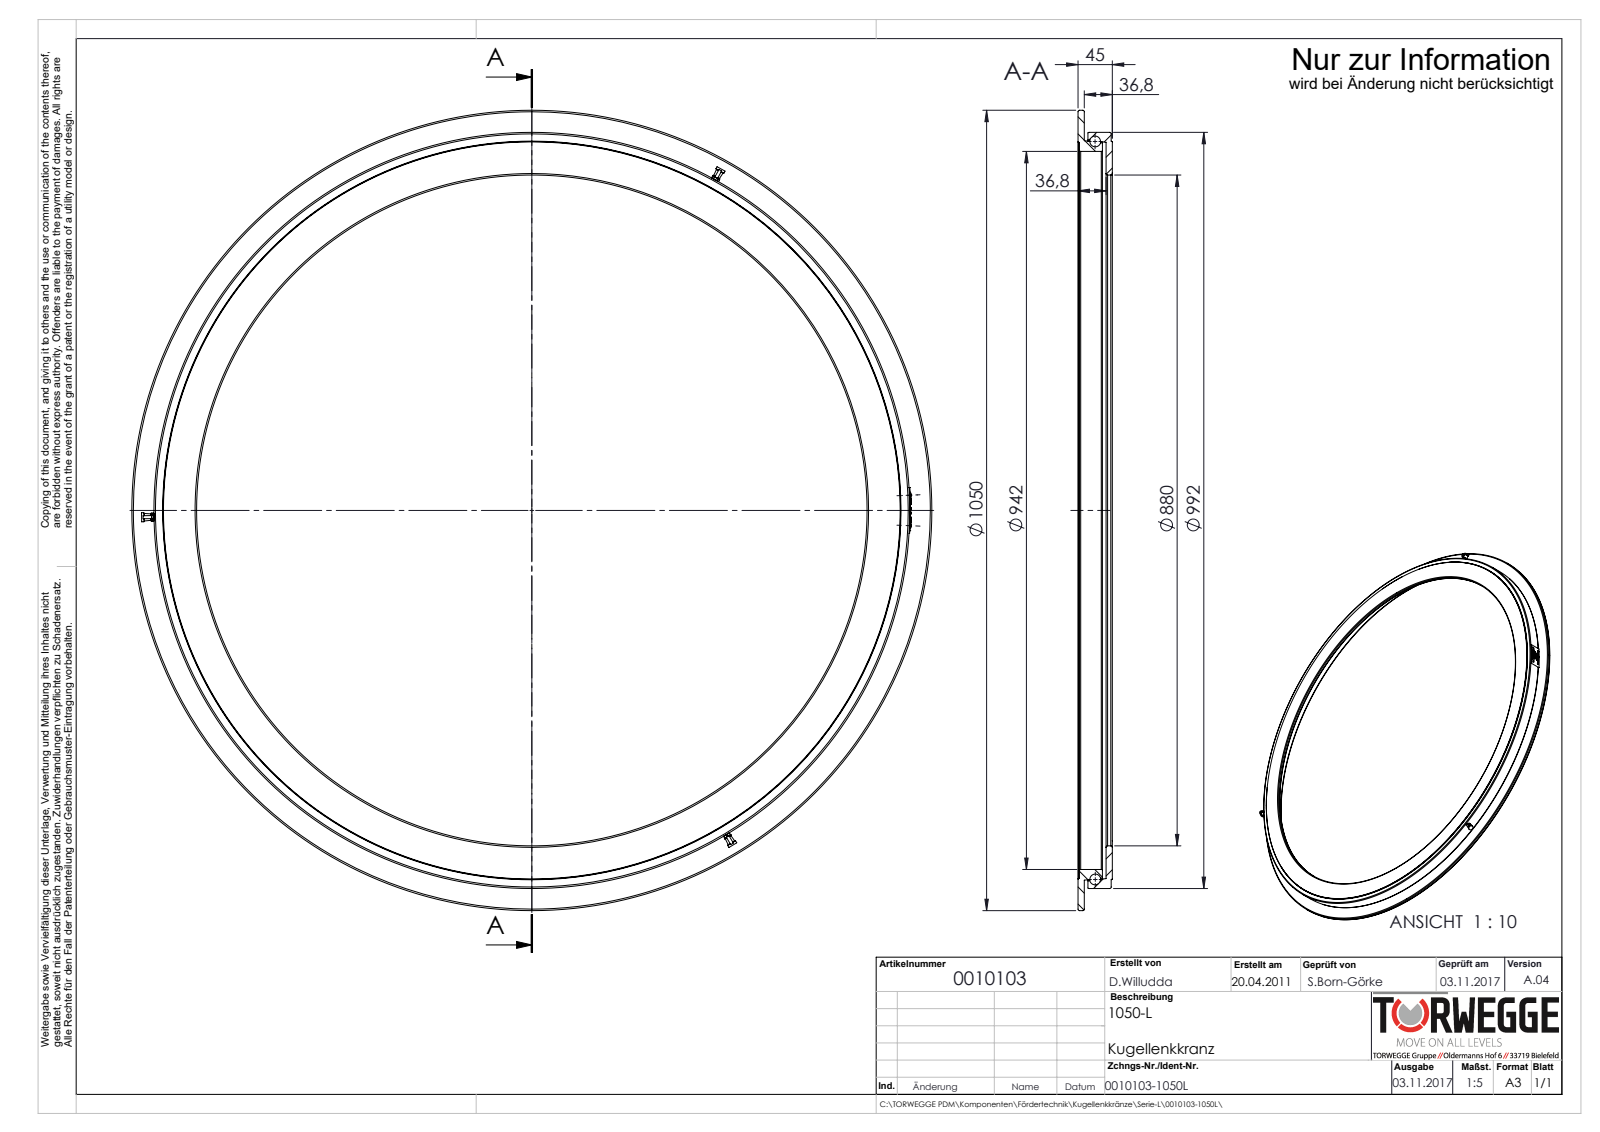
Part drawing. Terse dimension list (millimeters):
name: NT-0004300; 000012003; JS-1101-021; DK-750_V01 (+5 more)
written by: SolidWorks 2016 (AUTOMOTIVE_DESIGN)
unit: mm
bodies: 13 solids, 1101 faces (808 planar, 142 cylindrical, 151 other)
size: 1050 × 1050 × 45.08
volume: 3 879 000 mm³; area: 1 091 000 mm²
holes: 6× ⌀6, 5× ⌀1.5, 3× ⌀4, 3× ⌀7.5, 2× ⌀4.9, 2× ⌀5.5, 1× ⌀14.5, 1× ⌀880, 1× ⌀942, 1× ⌀966
bosses: 3× ⌀12, 2× ⌀7.5, 2× ⌀4.9, 2× ⌀4.7, 1× ⌀1050, 1× ⌀992, 1× ⌀968, 1× ⌀14.3
rounds: 3× R1.75, 3× R4.62, 3× R5, 3× R5.62, 1× R496.38, 1× R496.48
face distances: 8.2, 36.8, 28.6, 45, 4.8, 13, 32, 23.8, 6.7, 1.5
